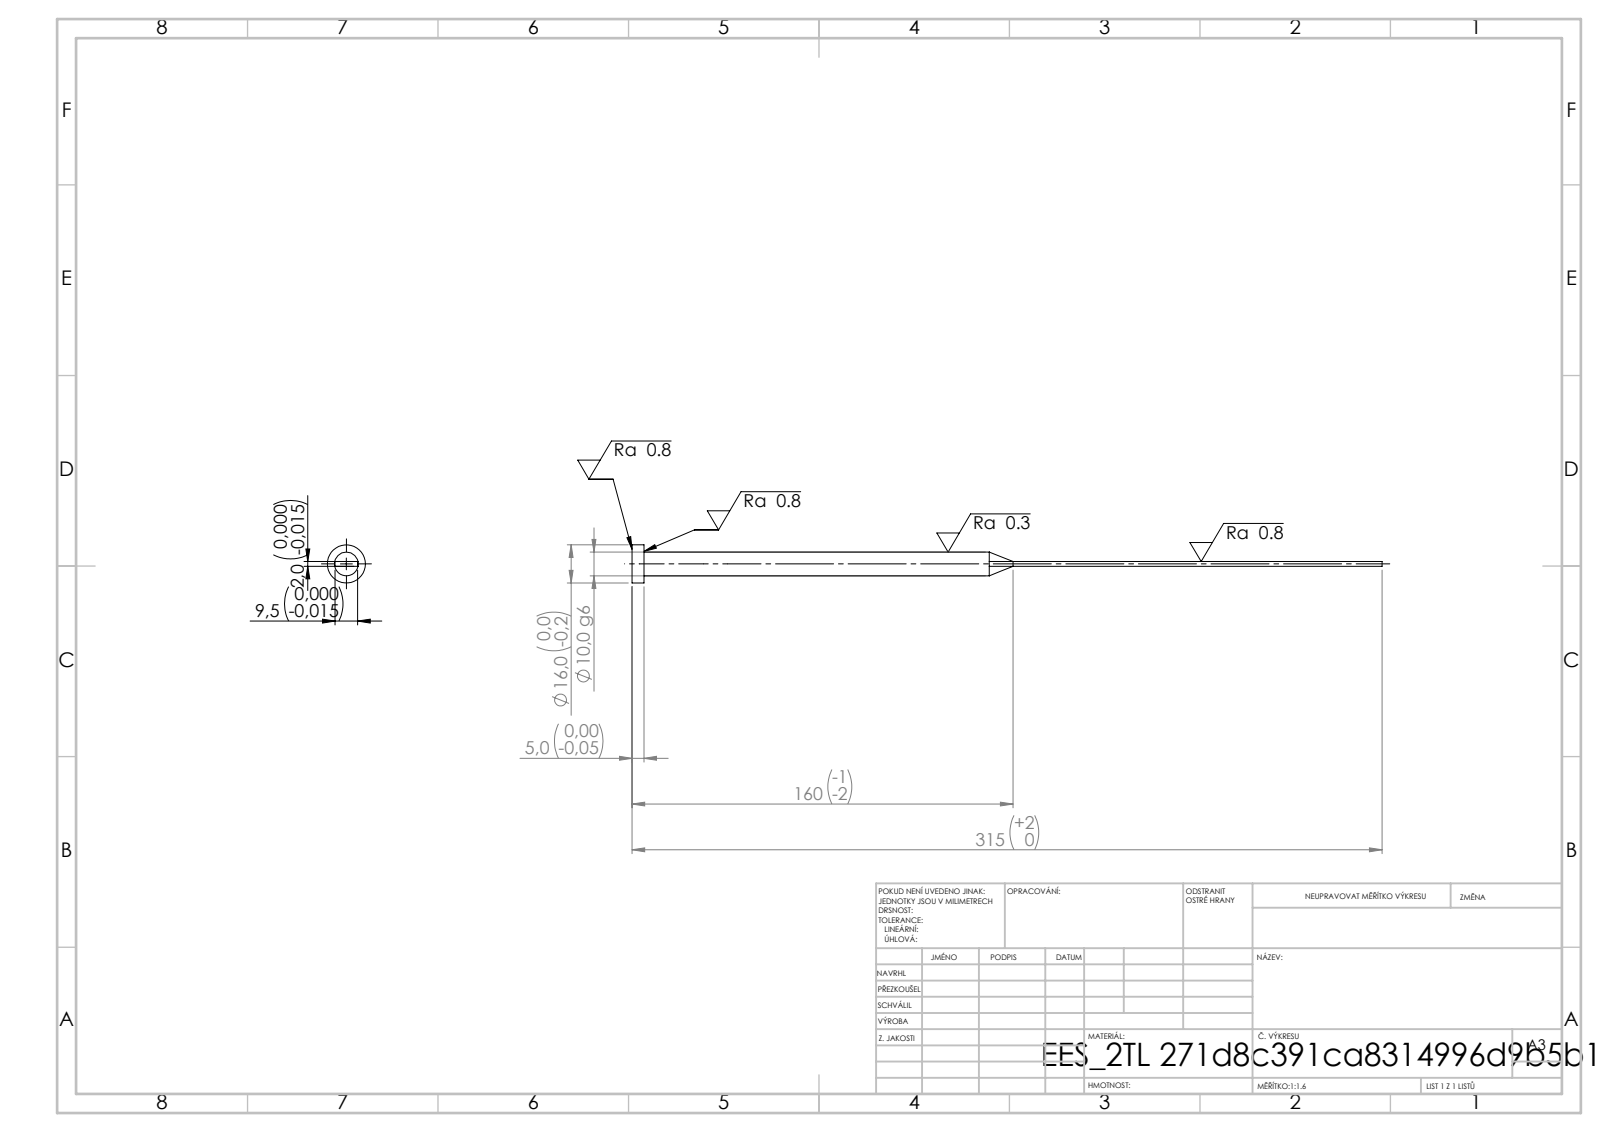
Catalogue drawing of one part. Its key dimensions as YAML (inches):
step_written_by: "SolidWorks 2019 (CONFIG_CONTROL_DESIGN)"
units: inches
bodies: {solids: 1, faces: 15, planar: 7, cylindrical: 4, other: 4}
overall_size: [12.402, 0.63, 0.63]
volume: 0.964
surface_area: 13.92
round_bosses_or_shafts:
  - {diameter: 0.63, count: 1}
  - {diameter: 0.394, count: 1}
face_to_face_distances: [0.079, 0.374, 0.197, 12.402, 12.205]
